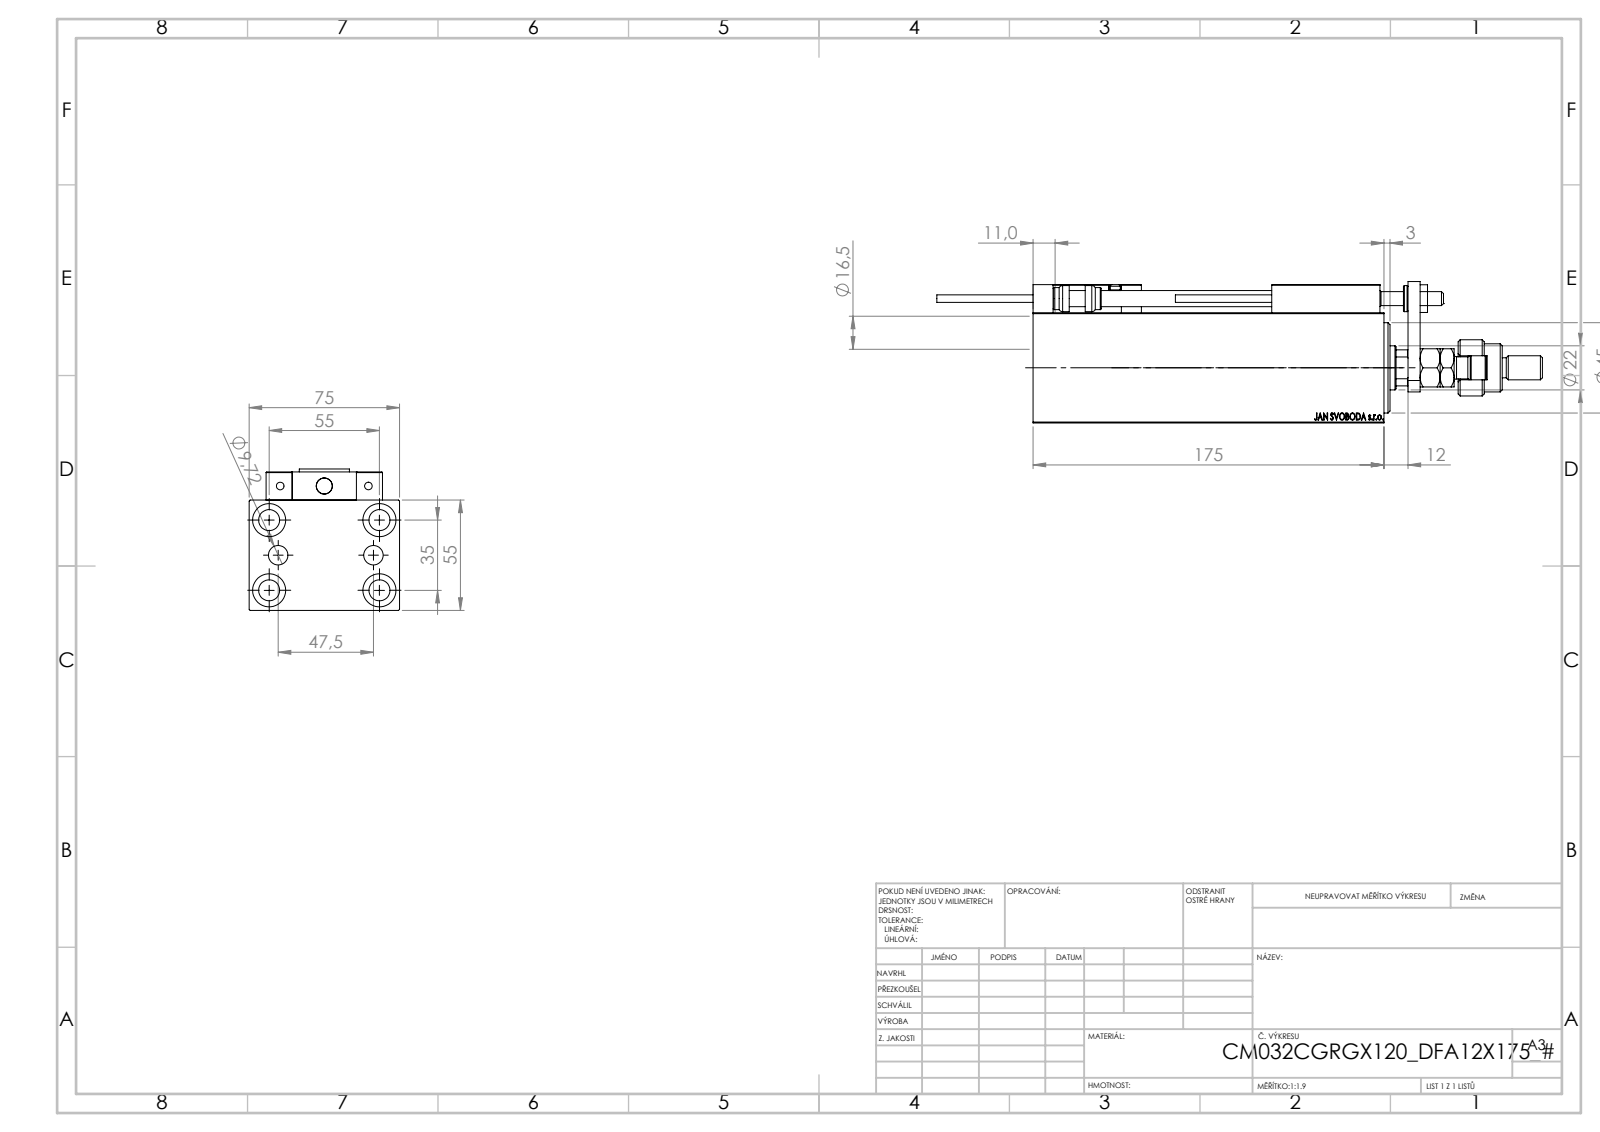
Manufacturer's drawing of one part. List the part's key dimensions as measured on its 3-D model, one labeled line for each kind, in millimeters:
Part name (STEP PRODUCT): X_Y_DFA; ALLEN BOLT D8; SWITCH_X_FRONT_BACK; TYC_L79 (+7 more)
STEP written by: SolidWorks 2019 (CONFIG_CONTROL_DESIGN)
Units: millimetres
Bodies: 25 solids, 1363 faces (588 planar, 197 cylindrical, 578 other)
Overall size (bounding box): 302 × 75 × 70.5
Volume: 669 799 mm³ · Surface area: 155 457 mm²
Round holes (diameter × count): ⌀4 ×6, ⌀8 ×5, ⌀10.5 ×5, ⌀16.5 ×5, ⌀3.2 ×4, ⌀5 ×2, ⌀9.72 ×2, ⌀7 ×1, ⌀22 ×1, ⌀25.5 ×1, ⌀32 ×1, ⌀34 ×1
Round bosses / shafts (diameter × count): ⌀11 ×2, ⌀5 ×2, ⌀3.8 ×2, ⌀28 ×1, ⌀24 ×1, ⌀18 ×1, ⌀13 ×1, ⌀12 ×1
Partial cylindrical surfaces — rounded edges, fillets, slot ends (radius × count): R0.3 ×30, R3 ×2, R9.75 ×1, R10.5 ×1
Main face-to-face distances: 55, 75, 14, 10, 18, 25, 6, 69, 12, 3
Hole centre spacings: 17.9, 32.6, 54.16, 11.37, 20, 23.75, 29.59, 29.69
